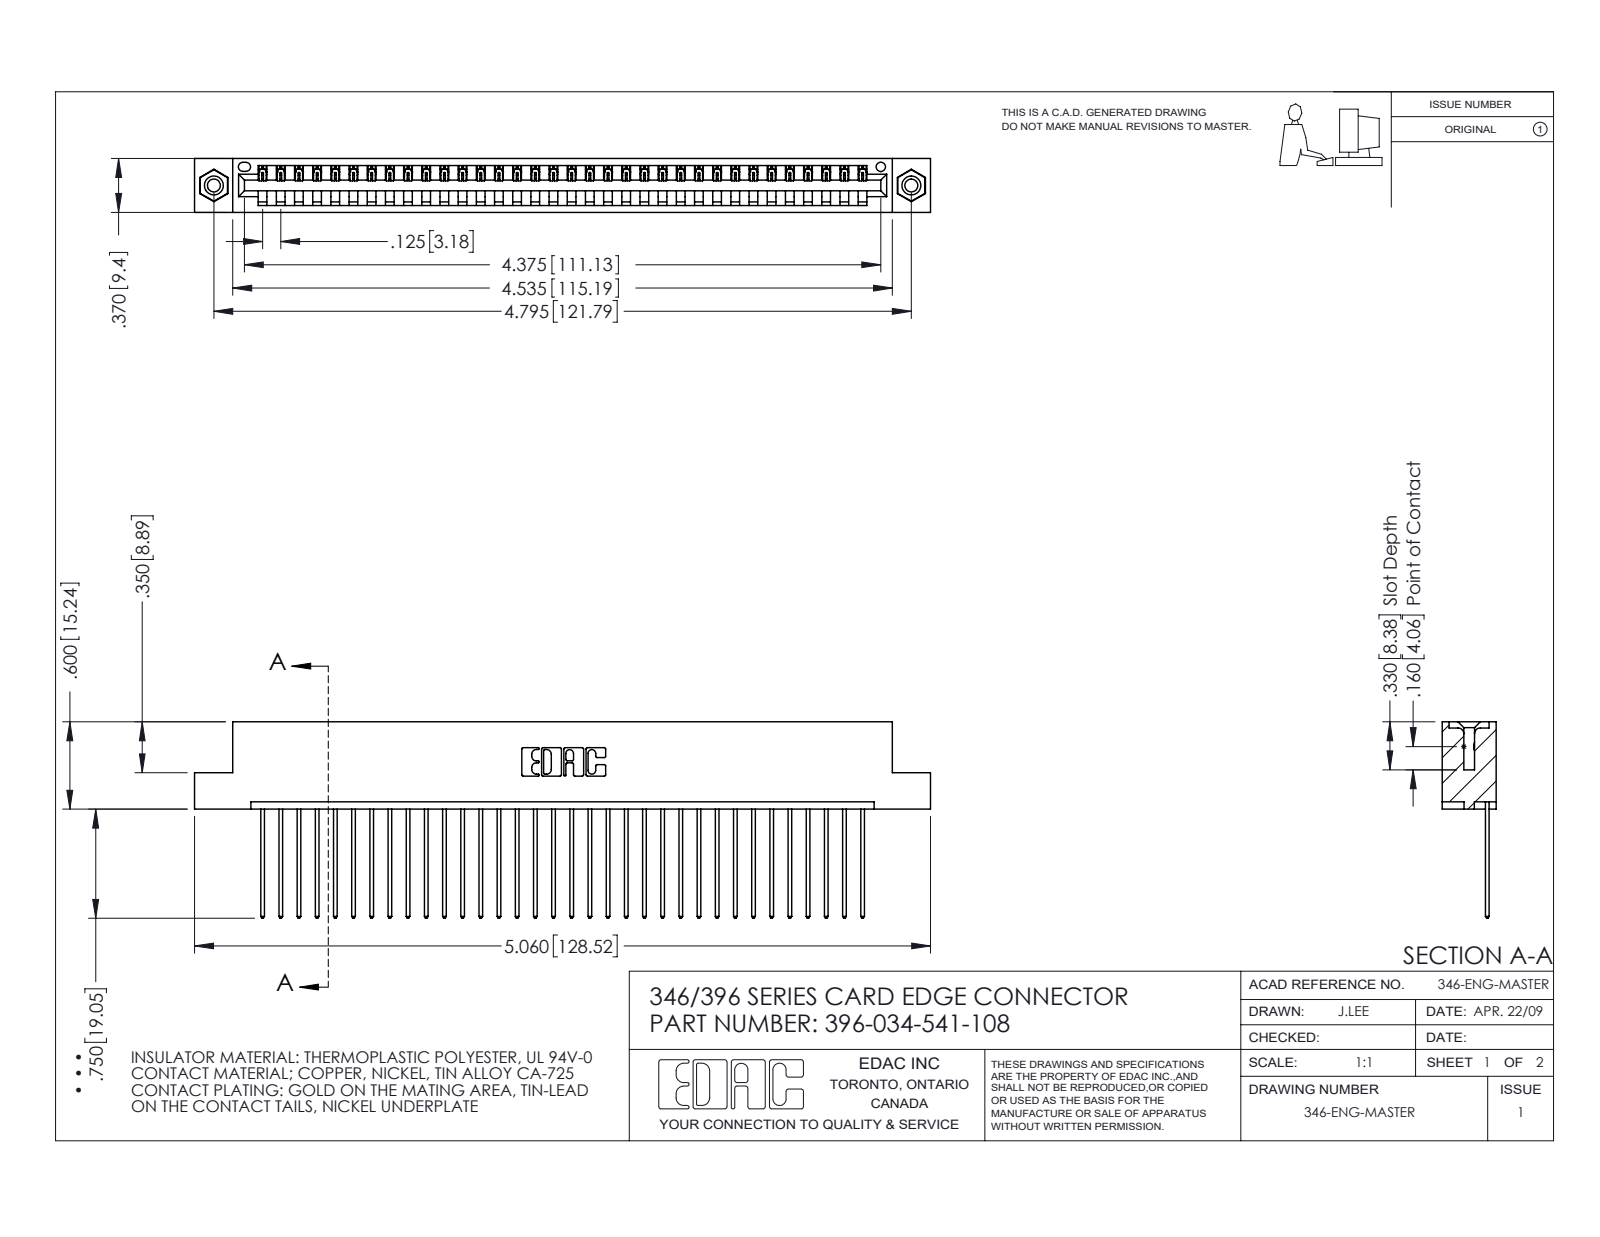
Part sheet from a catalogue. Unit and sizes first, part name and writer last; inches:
Units: inches
Overall size (bounding box): 5.06 × 1.35 × 0.37
Round holes (diameter × count): ⌀0.089 ×2, ⌀0.125 ×2, ⌀0.156 ×2, ⌀0.064 ×1
Round bosses / shafts (diameter × count): ⌀0.155 ×2
Partial cylindrical surfaces — rounded edges, fillets, slot ends (radius × count): R0.006 ×68, R0.01 ×68, R0.01 ×22, R0.007 ×6, R0.031 ×6, R0.026 ×3, R0.031 ×2, R0.04 ×2
Main face-to-face distances: 0.048, 0.322, 0.37, 0.25, 0.072, 0.298, 0.025, 0.148, 0.222, 0.1
Hole centre spacings: 0.246, 4.587, 4.795
Volume: 0.754 in³ · Surface area: 24.87 in²
Bodies: 37 solids, 2154 faces (1468 planar, 670 cylindrical, 16 other)
Part name (STEP PRODUCT): 396-034-541-108; 345-292-001_345-293-141; 345-250-001_345-250-003-102; 346 Part_Flush Mounting Lugs - 0.156 Dia-TI
STEP written by: SolidWorks 2016 (CONFIG_CONTROL_DESIGN)
